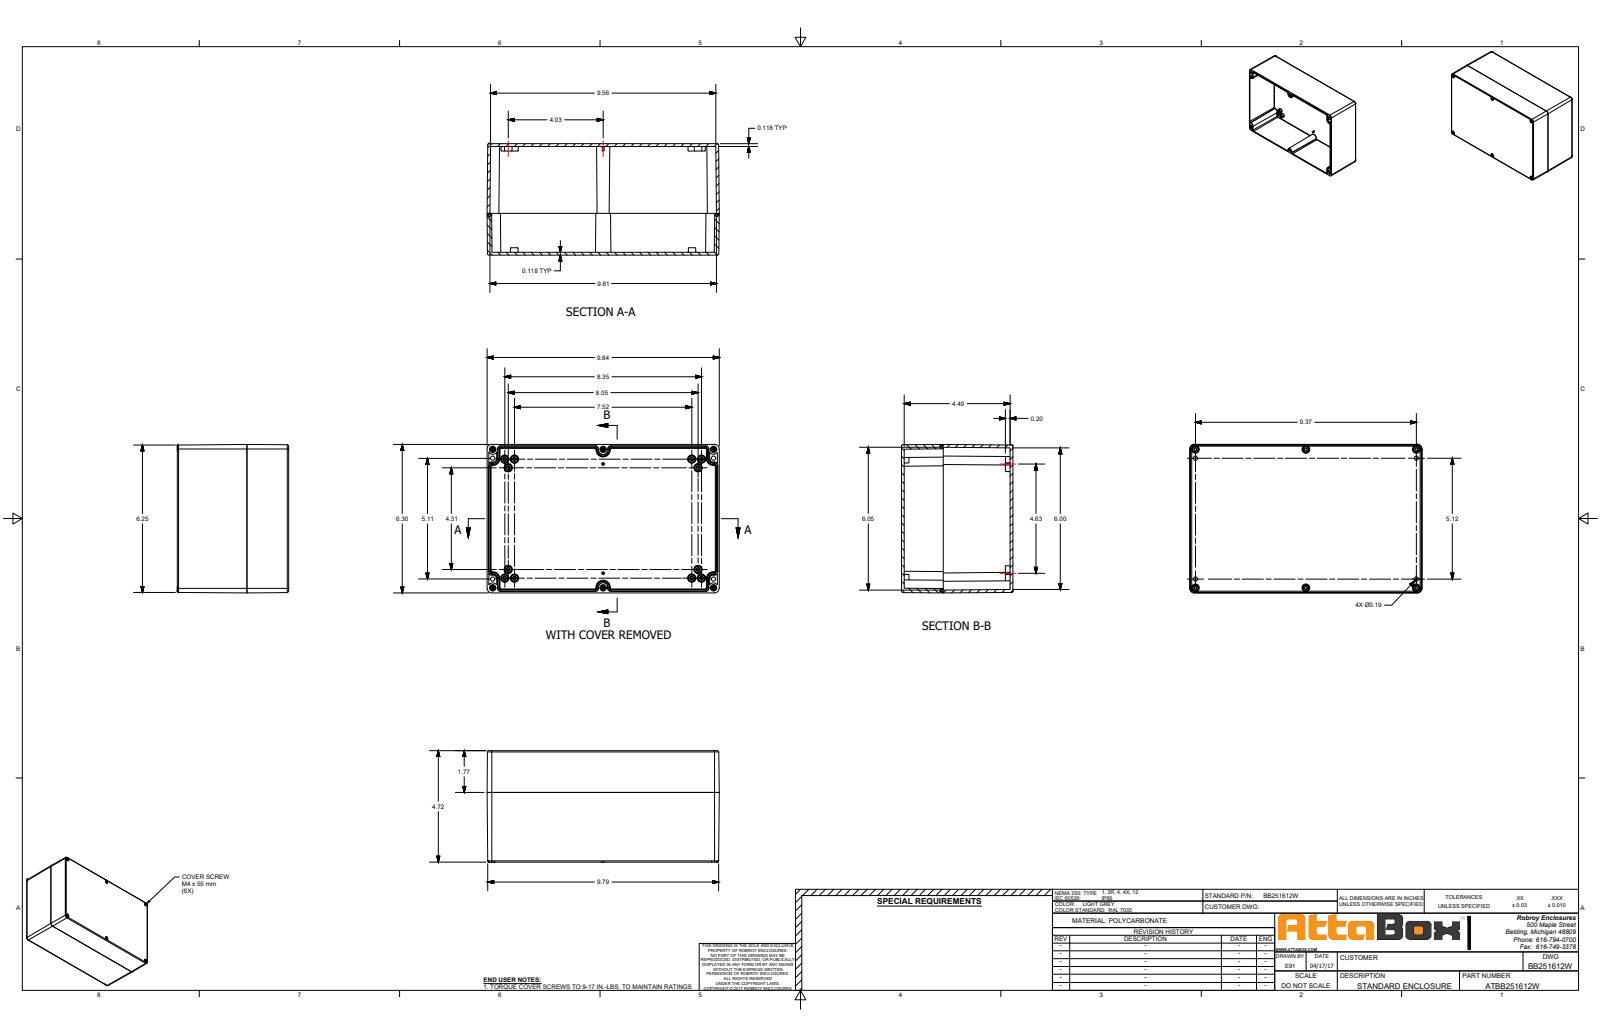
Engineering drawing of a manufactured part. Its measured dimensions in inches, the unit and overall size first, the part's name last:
Units: inches
Overall size (bounding box): 9.843 × 6.299 × 4.726
Round holes (diameter × count): ⌀0.128 ×6, ⌀0.177 ×6, ⌀0.193 ×6, ⌀0.201 ×6, ⌀0.276 ×6, ⌀0.283 ×6, ⌀0.323 ×6, ⌀0.185 ×4
Round bosses / shafts (diameter × count): ⌀0.268 ×6, ⌀0.173 ×6, ⌀0.157 ×6, ⌀0.13 ×6
Partial cylindrical surfaces — rounded edges, fillets, slot ends (radius × count): R0.049 ×40, R0.039 ×20, R0.059 ×16, R0.167 ×16, R0.004 ×12, R0.02 ×10, R0.102 ×6, R0.124 ×6
Main face-to-face distances: 0.118, 4.606, 4.724, 4.488, 0.124, 6.175, 6.299, 6.112, 0.187, 5.988
Hole centre spacings: 0.374, 4.685, 4.7, 5.492, 7.219, 7.507, 9.37, 9.378
Volume: 38.36 in³ · Surface area: 620.3 in²
Bodies: 15 solids, 2425 faces (901 planar, 588 cylindrical, 936 other)
Part name (STEP PRODUCT): BB251612W
STEP written by: SolidWorks 2018 (AUTOMOTIVE_DESIGN)
